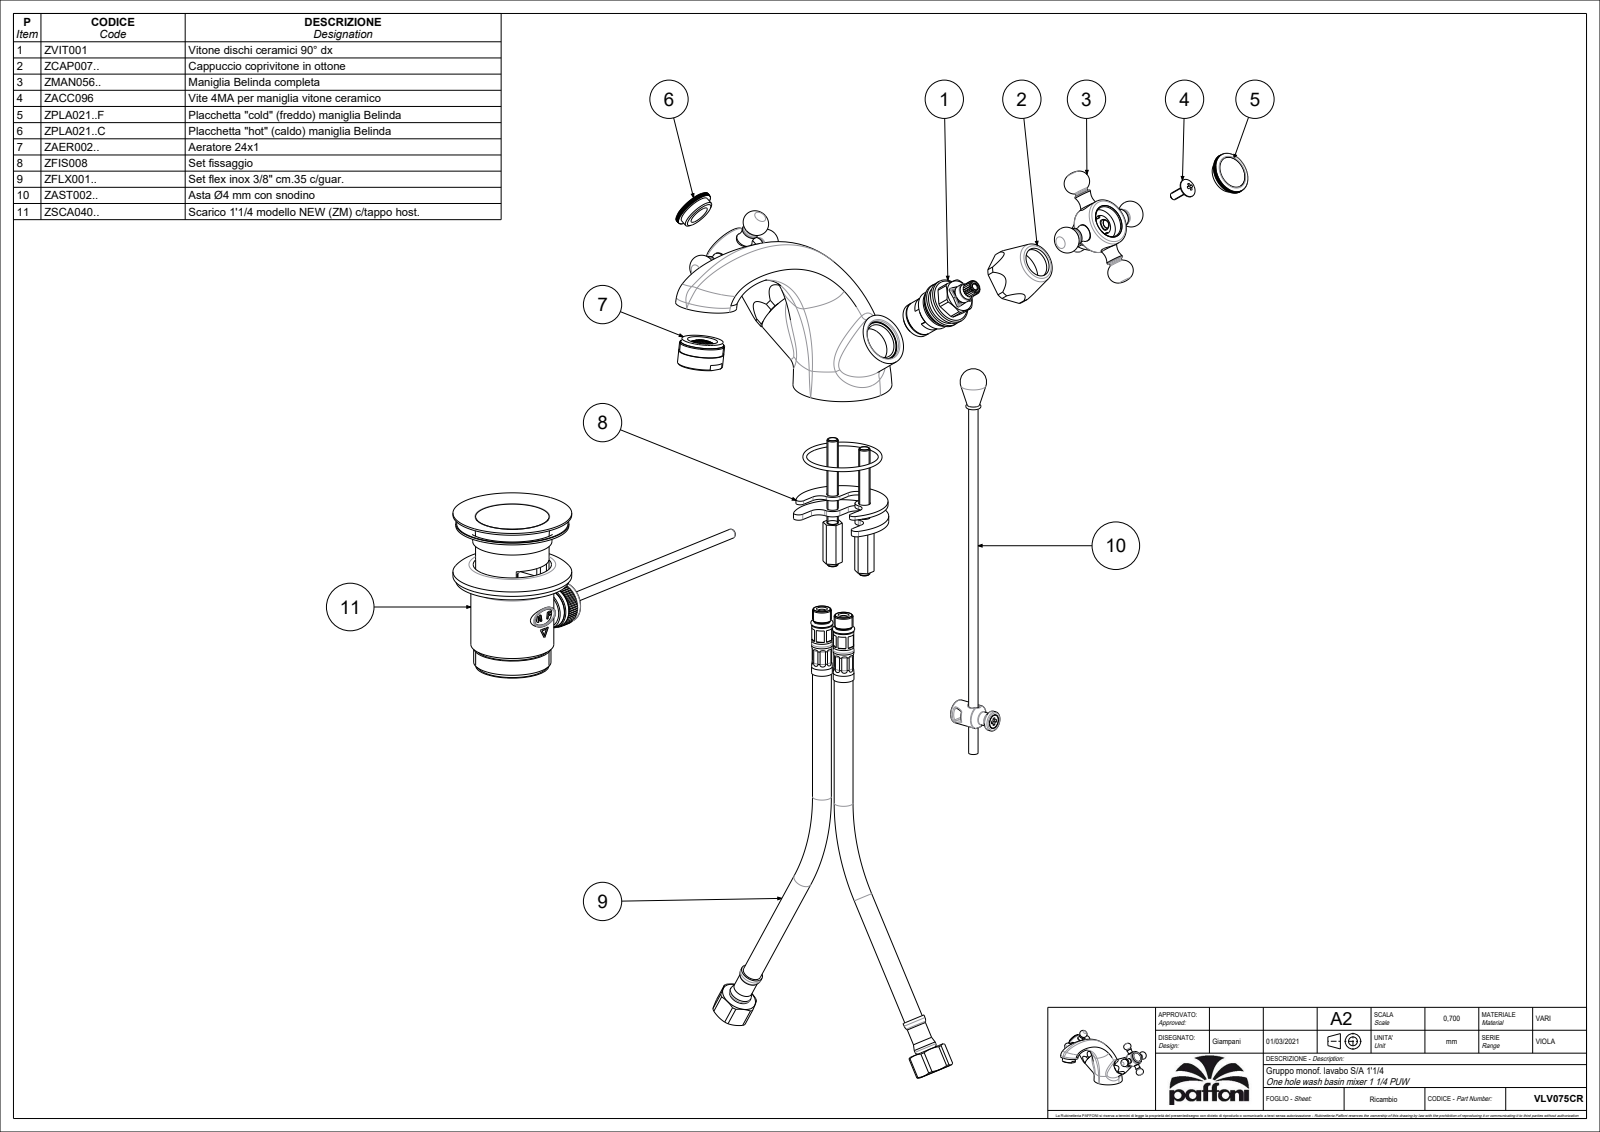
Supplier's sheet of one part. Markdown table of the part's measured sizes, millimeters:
| quantity | value |
| --- | --- |
| part name | VLV075CR |
| STEP written by | CREO PARAMETRIC BY PTC INC, 2020044 (CONFIG_CONTROL_DESIGN) |
| units | millimeters |
| bodies | 3 solids, 1031 faces (490 planar, 320 cylindrical, 221 other) |
| overall size | 180.18 × 154.8 × 98.4 |
| volume | 236 466 mm³ |
| surface area | 47 689 mm² |
| round holes (diameter × count) | 5.5 × 3, 7.75 × 2, 8 × 2, 9 × 2, 11 × 2, 18.6 × 2, 21.5 × 2, 42.5 × 1 |
| round bosses / shafts (diameter × count) | 9 × 6, 7 × 6, 27.5 × 2, 25 × 2, 14 × 2, 13 × 2, 37.5 × 1, 24 × 1 |
| partial cylindrical surfaces (radius × count) | 11 × 2, 14.5 × 2 |
| main face-to-face distances | 35.32, 26.5, 57.2, 21.88, 7.7, 11.2, 24.12, 46, 22, 15 |
| hole center spacings | 10.97, 12.08, 13.46, 13.6, 22.3, 22.61, 13, 15 |
